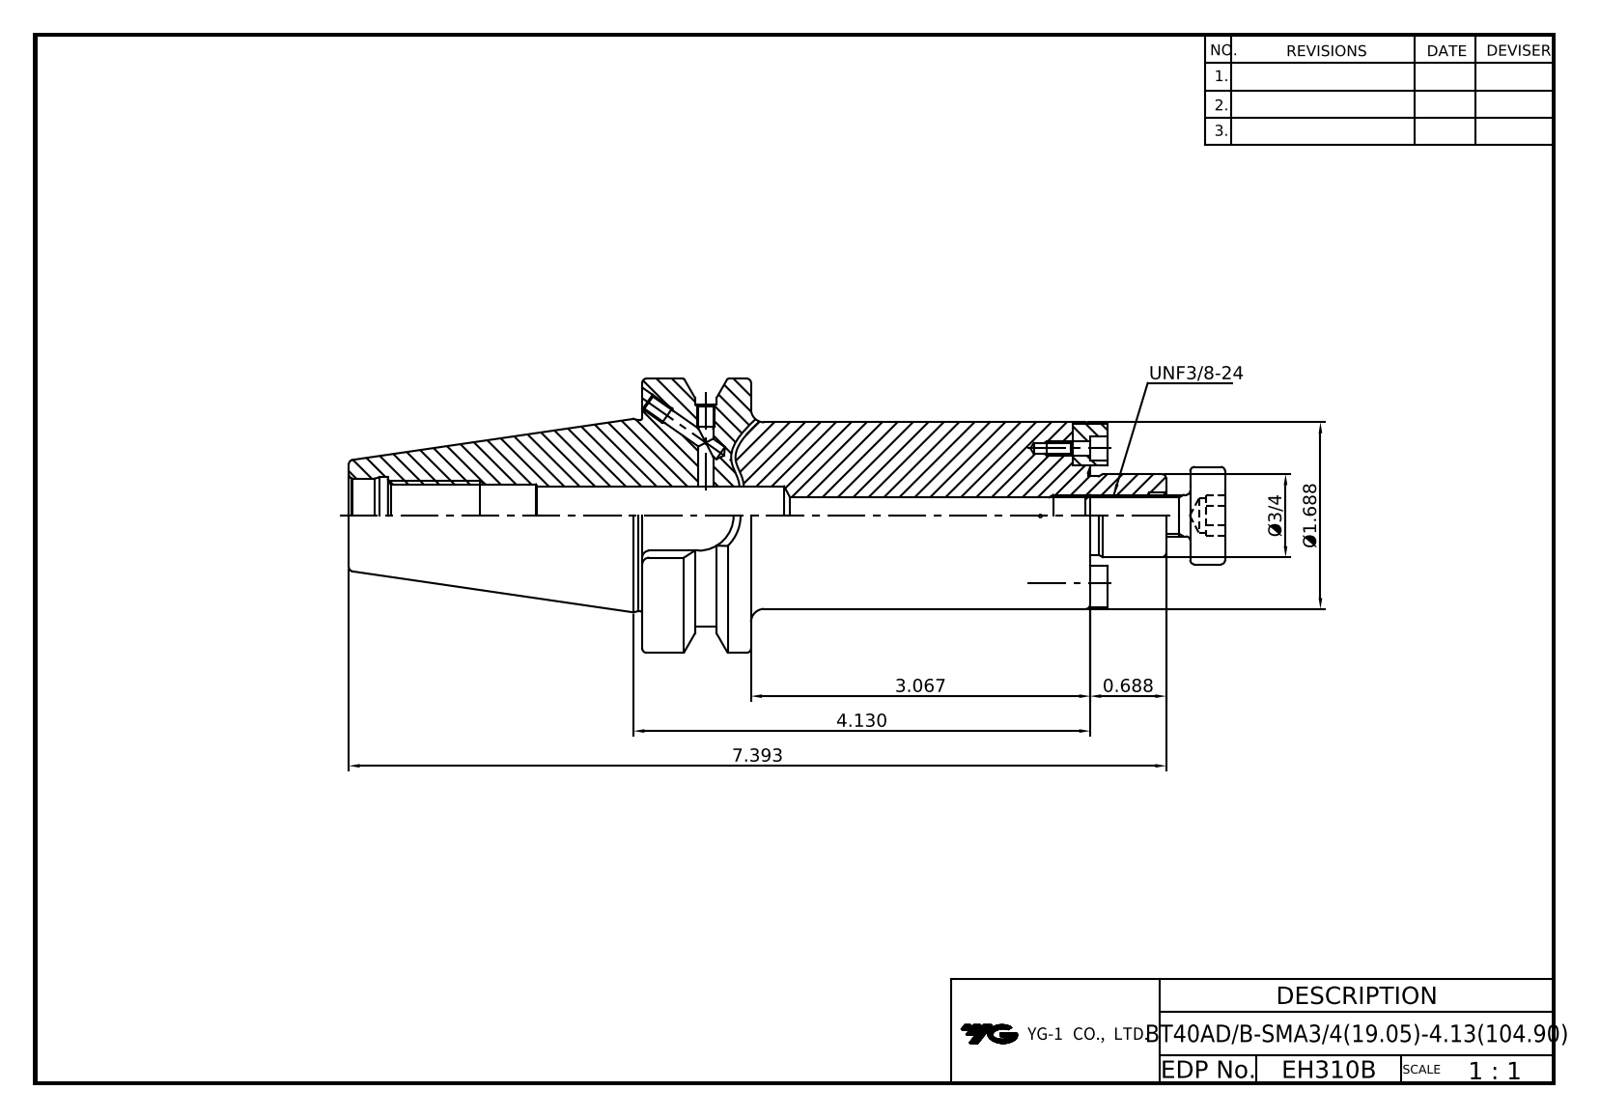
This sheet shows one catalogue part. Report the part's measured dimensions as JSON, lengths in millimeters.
{"part_name": "LO-BT40ADB-SMA19.05-104.9; DRIVE KEY-7.93x7.93x9.5; HEX'' WRENCH BOLT-UNC#5-40x5_16L; COLLAR BOLT-UNF3_8-24x24L", "step_written_by": "Autodesk Inventor 2025 (AP242_MANAGED_MODEL_BASED_3D_ENGINEERING_MIM_LF)", "units": "millimeters", "bodies": {"solids": 6, "faces": 147, "planar": 72, "cylindrical": 44, "other": 31}, "overall_size": [205.8, 63, 63], "volume_mm3": 235000, "surface_area_mm2": 41270, "round_holes": [[3.3, 4], [4, 4], [2.5, 2], [3.3, 2], [5.4, 2], [8, 1], [8.4, 1], [10.5, 1], [13.8, 1], [17, 1], [17.6, 1]], "round_bosses_or_shafts": [[5.2, 2], [3.2, 2], [63, 1], [52.6, 1], [44, 1], [42.9, 1], [22.4, 1], [19.1, 1]], "partial_cylinders_radius": [[4, 2], [8.1, 1]], "face_to_face_distances": [25, 102.9, 77.9, 45.2, 138.4, 113.4, 35.5, 98.9, 73.9, 4], "hole_center_spacings": [15.5, 30.9]}
